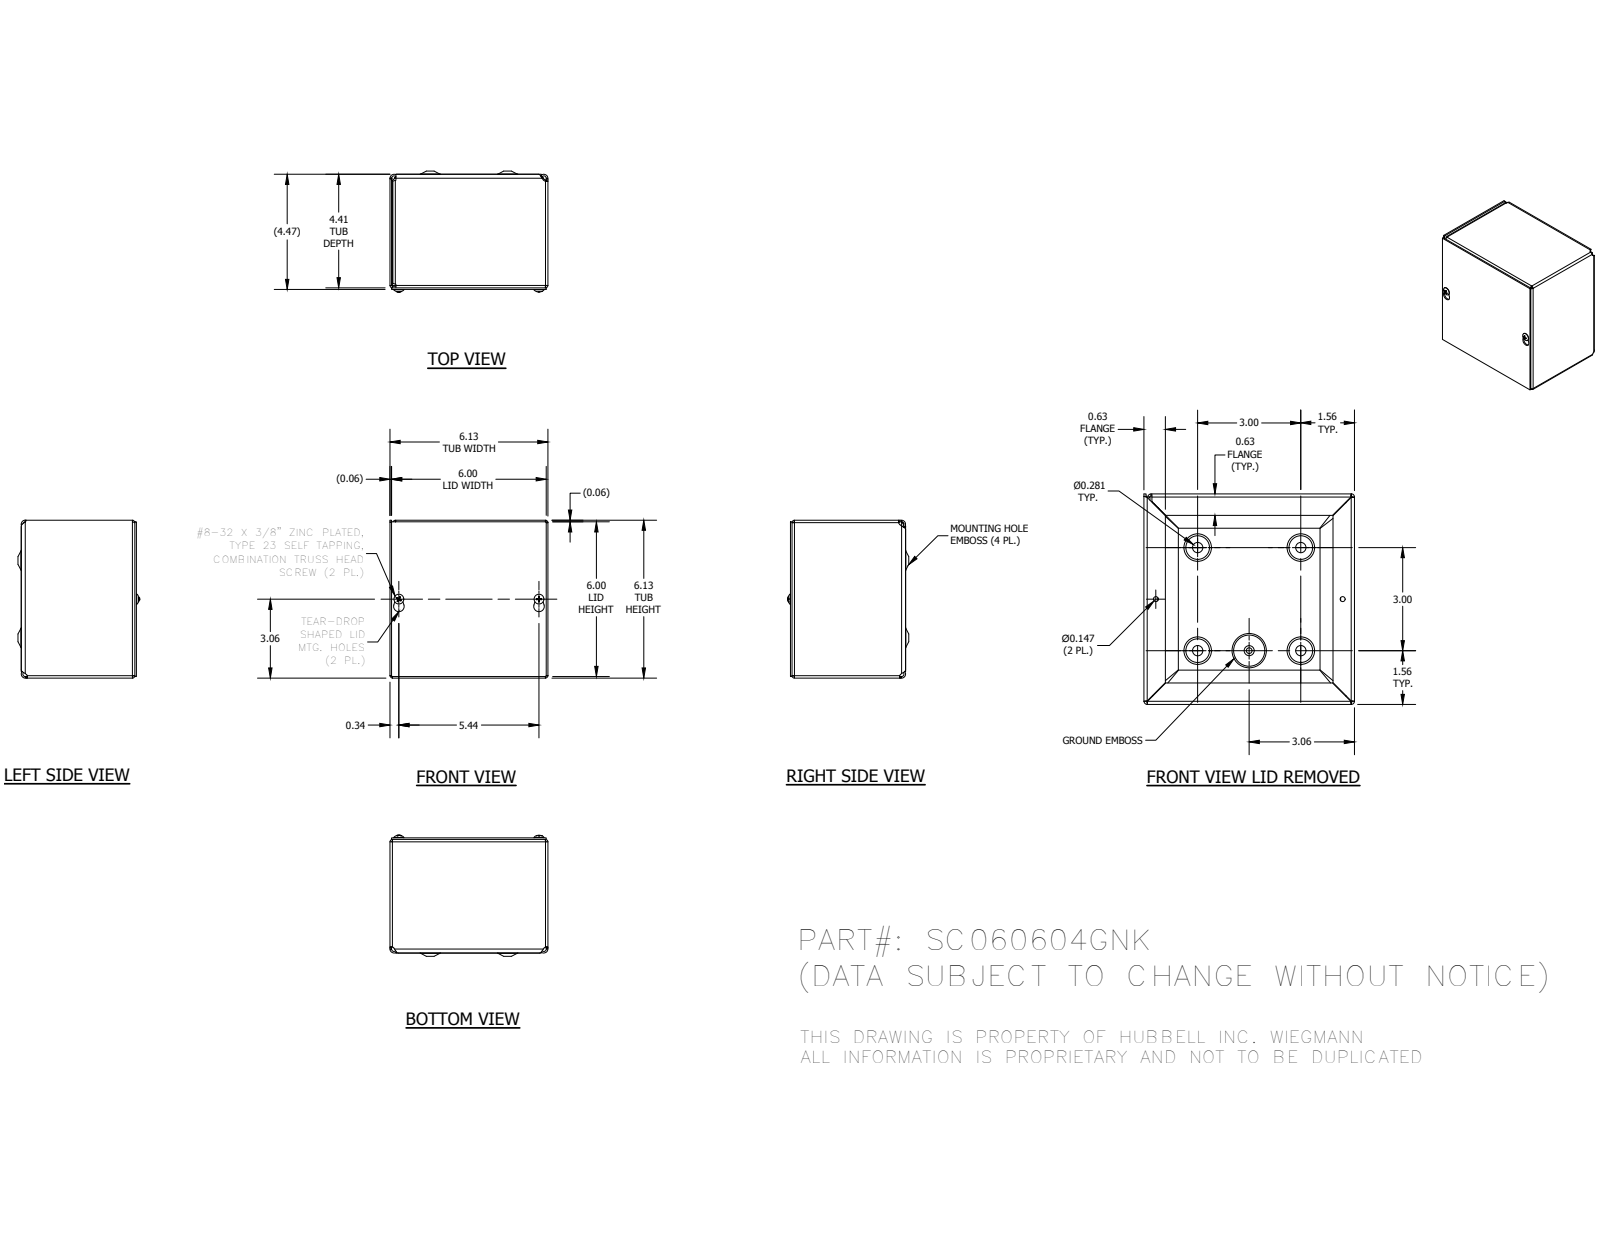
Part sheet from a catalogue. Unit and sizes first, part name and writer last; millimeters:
Units: millimetres
Overall size (bounding box): 155.57 × 155.57 × 119.2
Round holes (diameter × count): ⌀7.62 ×4, ⌀3.73 ×2, ⌀4.19 ×1
Round bosses / shafts (diameter × count): ⌀9.75 ×2, ⌀4.17 ×2, ⌀5.8 ×1
Partial cylindrical surfaces — rounded edges, fillets, slot ends (radius × count): R0.79 ×8, R2.37 ×8, R1.4 ×4, R1.57 ×4, R2.38 ×4, R2.97 ×4, R3.15 ×4, R3.96 ×4
Main face-to-face distances: 1.57, 154, 110.32, 152.43, 1.58, 111.89, 1.59, 111.91, 113.48, 155.58
Hole centre spacings: 76.2, 38.1, 85.19, 107.76, 113.72, 49.07, 49.08, 49.1
Volume: 208 618 mm³ · Surface area: 269 837 mm²
Bodies: 5 solids, 294 faces (109 planar, 63 cylindrical, 122 other)
Part name (STEP PRODUCT): SC0606GNKBKP; SC060604GNKWRA; SC0606GNKLID; 34056 (+1 more)
STEP written by: Autodesk Inventor 2014 (AUTOMOTIVE_DESIGN)
